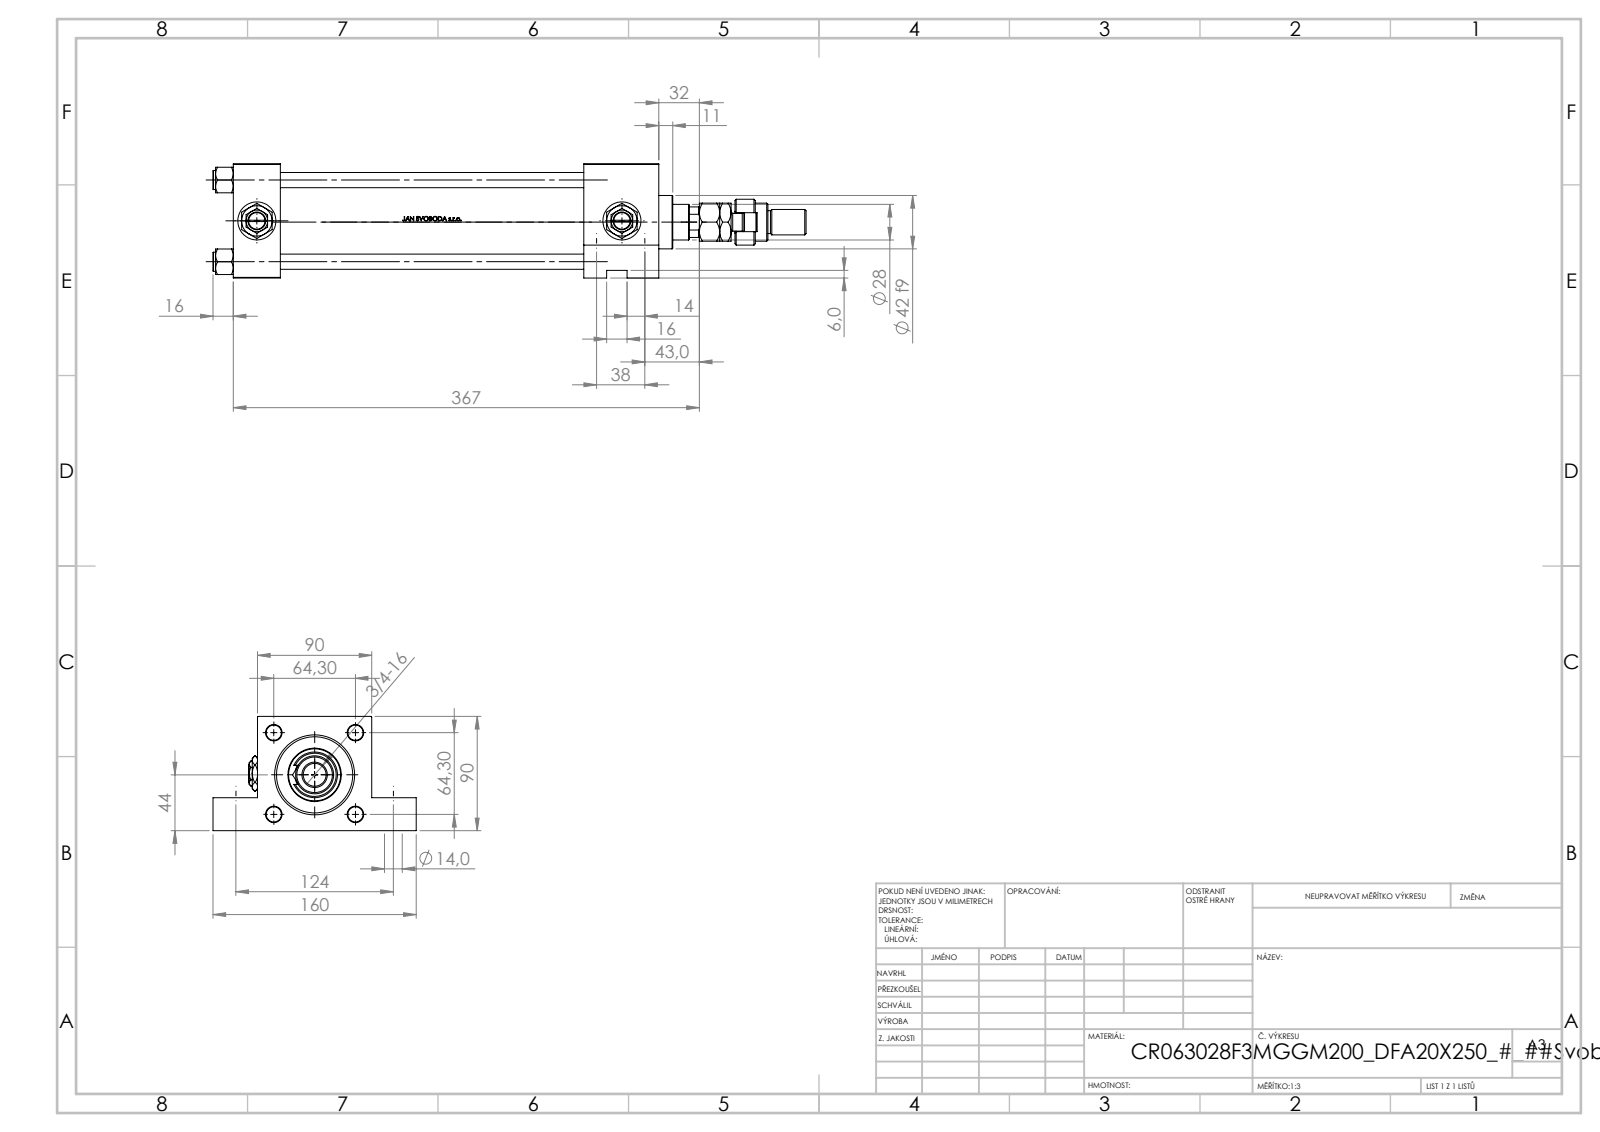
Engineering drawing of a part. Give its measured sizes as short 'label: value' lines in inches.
name: V215CR_F_TYCINKA; V215CR_F_Body; V215CR_VCP_F; NUT_M5_F (+4 more)
written by: SolidWorks 2019 (CONFIG_CONTROL_DESIGN)
unit: in
bodies: 15 solids, 1288 faces (513 planar, 149 cylindrical, 626 other)
size: 18.386 × 6.299 × 3.543
volume: 83.97 in³; area: 510.9 in²
holes: 4× ⌀0.472, 4× ⌀0.551, 4× ⌀0.825, 4× ⌀1.181, 3× ⌀0.276, 1× ⌀0.728, 1× ⌀1.102, 1× ⌀1.22, 1× ⌀1.969, 1× ⌀2.362, 1× ⌀2.48
bosses: 4× ⌀0.591, 1× ⌀2.717, 1× ⌀1.654, 1× ⌀1.417, 1× ⌀1.181, 1× ⌀0.866, 1× ⌀0.787, 1× ⌀0.709
rounds: 1× R0.295, 1× R0.472, 1× R0.531
face distances: 3.543, 1.457, 13.189, 11.732, 2.323, 10.866, 9.409, 1.024, 2.52, 1.378
hole spacings: 2.531, 1.496, 1.763, 1.818, 2.472, 2.678, 3.58, 4.882
